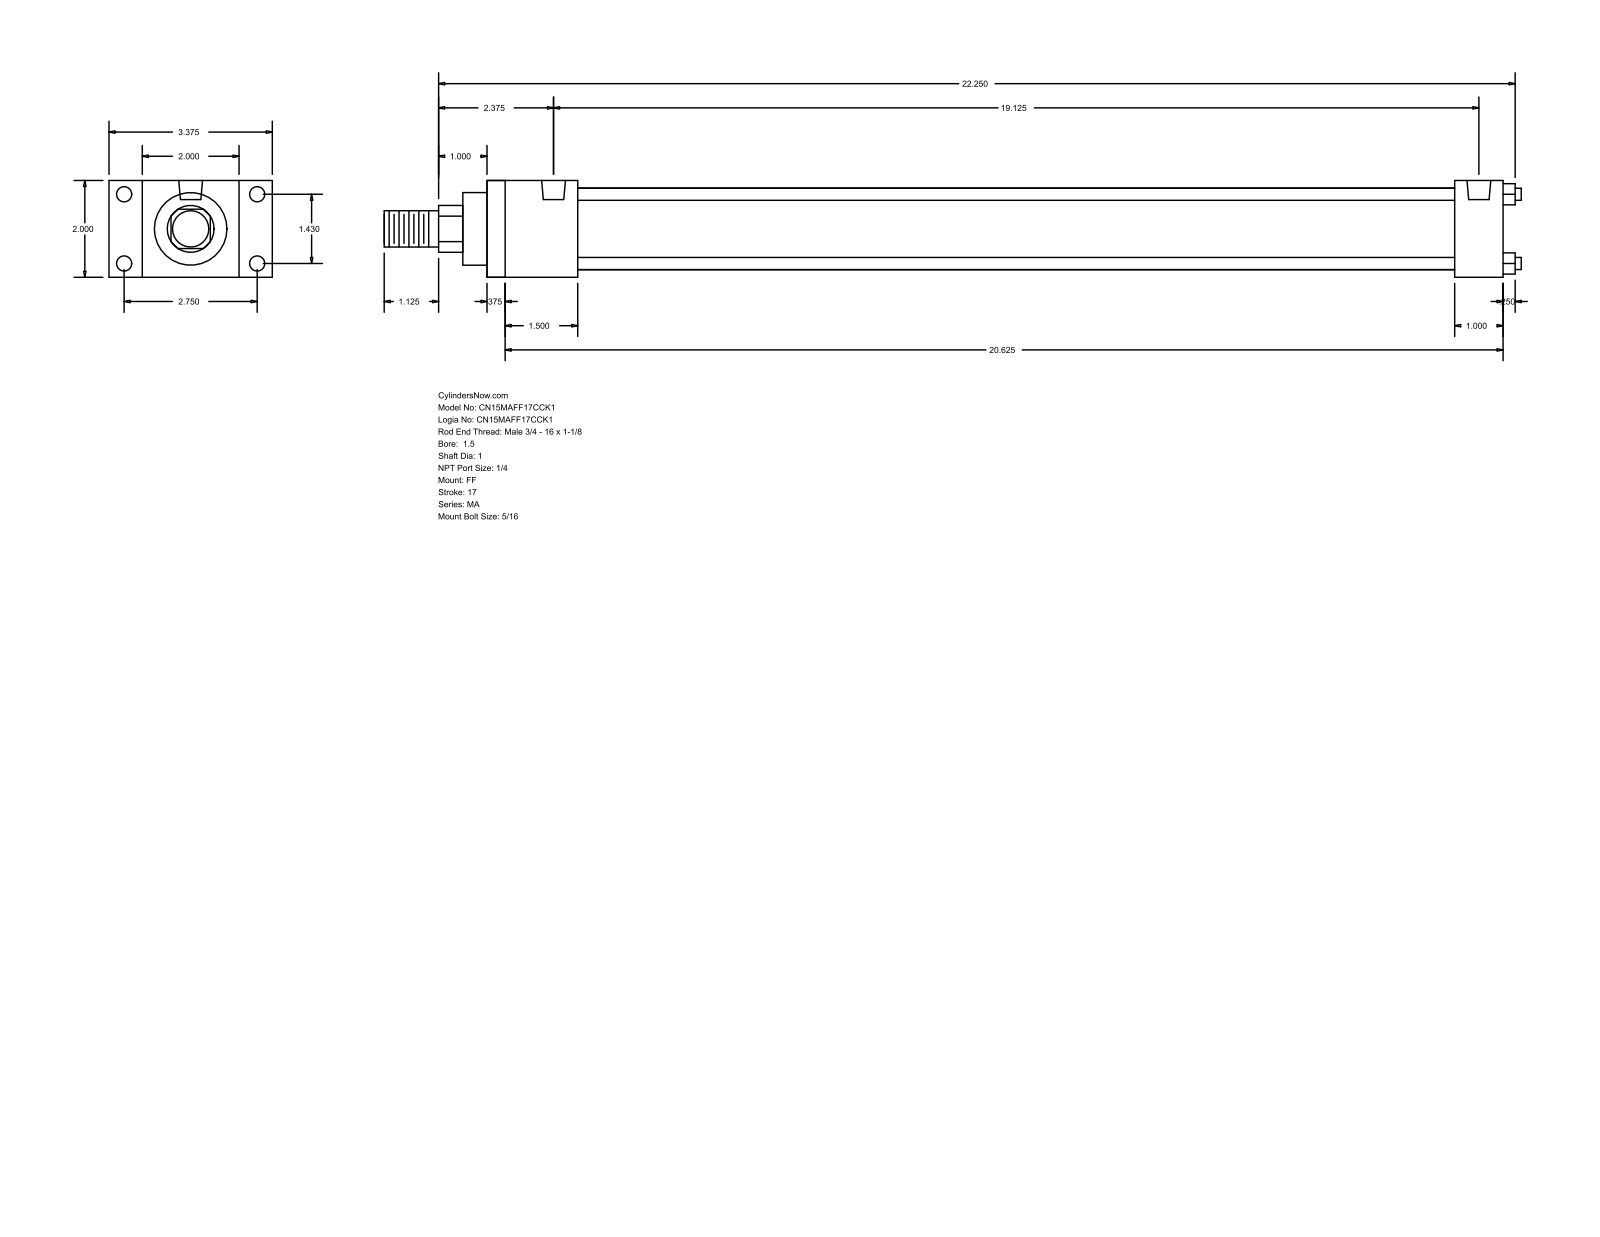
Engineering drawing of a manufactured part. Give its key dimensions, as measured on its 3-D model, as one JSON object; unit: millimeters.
{"part_name": "MA_FF__0150_1", "step_written_by": "GSSL Pune (CONFIG_CONTROL_DESIGN)", "units": "millimeters", "bodies": {"solids": 0, "faces": 92, "planar": 64, "cylindrical": 28, "other": 0}, "overall_size": [596.9, 85.72, 50.8], "round_holes": [[7.94, 8], [12.49, 2]], "round_bosses_or_shafts": [[6.35, 4], [42.93, 1], [38.1, 1], [25.4, 1], [19.05, 1]], "partial_cylinders_radius": [[12.29, 1]], "face_to_face_distances": [50.8, 533.4, 9.52, 523.88, 25.4, 47.63, 508, 38.11, 498.48, 460.37], "hole_center_spacings": [36.32, 69.84, 78.72, 485.77]}
